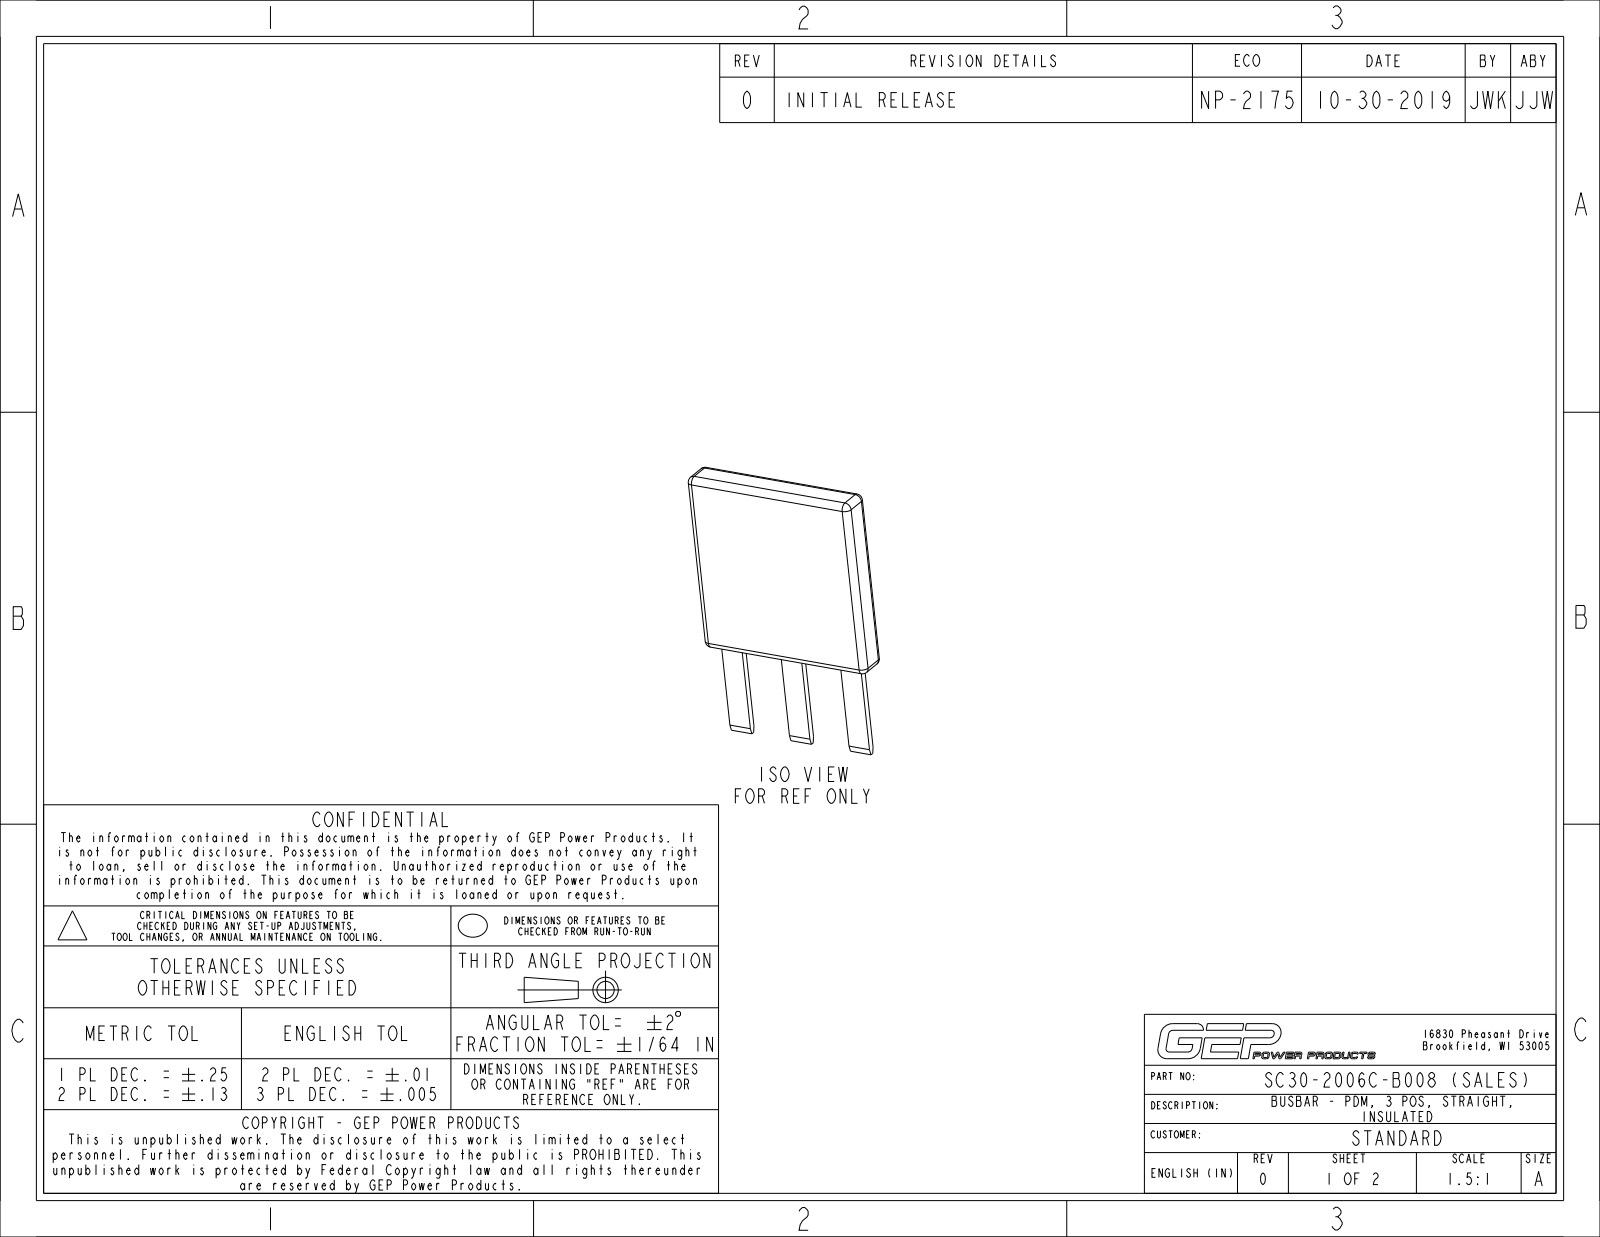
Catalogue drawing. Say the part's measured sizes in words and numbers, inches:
The part is named "PC29-2004C-C000_NCF; PC29-2004C-C000_MOLD; PC30-2006C-B008_NCF_ASM; SC30-2006C-B008_NCF_ASM". Its 3-D file was written by "CREO PARAMETRIC BY PTC INC, 2017110 (CONFIG_CONTROL_DESIGN)". It is 2 solids with 57 faces: 37 planar, 12 cylindrical and 8 other. Overall it measures 1.31 by 0.87 by 0.152 inches. Its volume is 0.118 cubic inches and its surface area 4.836 square inches. Partial cylindrical surfaces (rounded edges, fillets, slot ends): 12 of radius 0.03. The main face-to-face distances are 0.032, 0.06, 0.06, 0.092, 0.152, 0.092, 0.81, 0.87, 0.75, 0.87.
